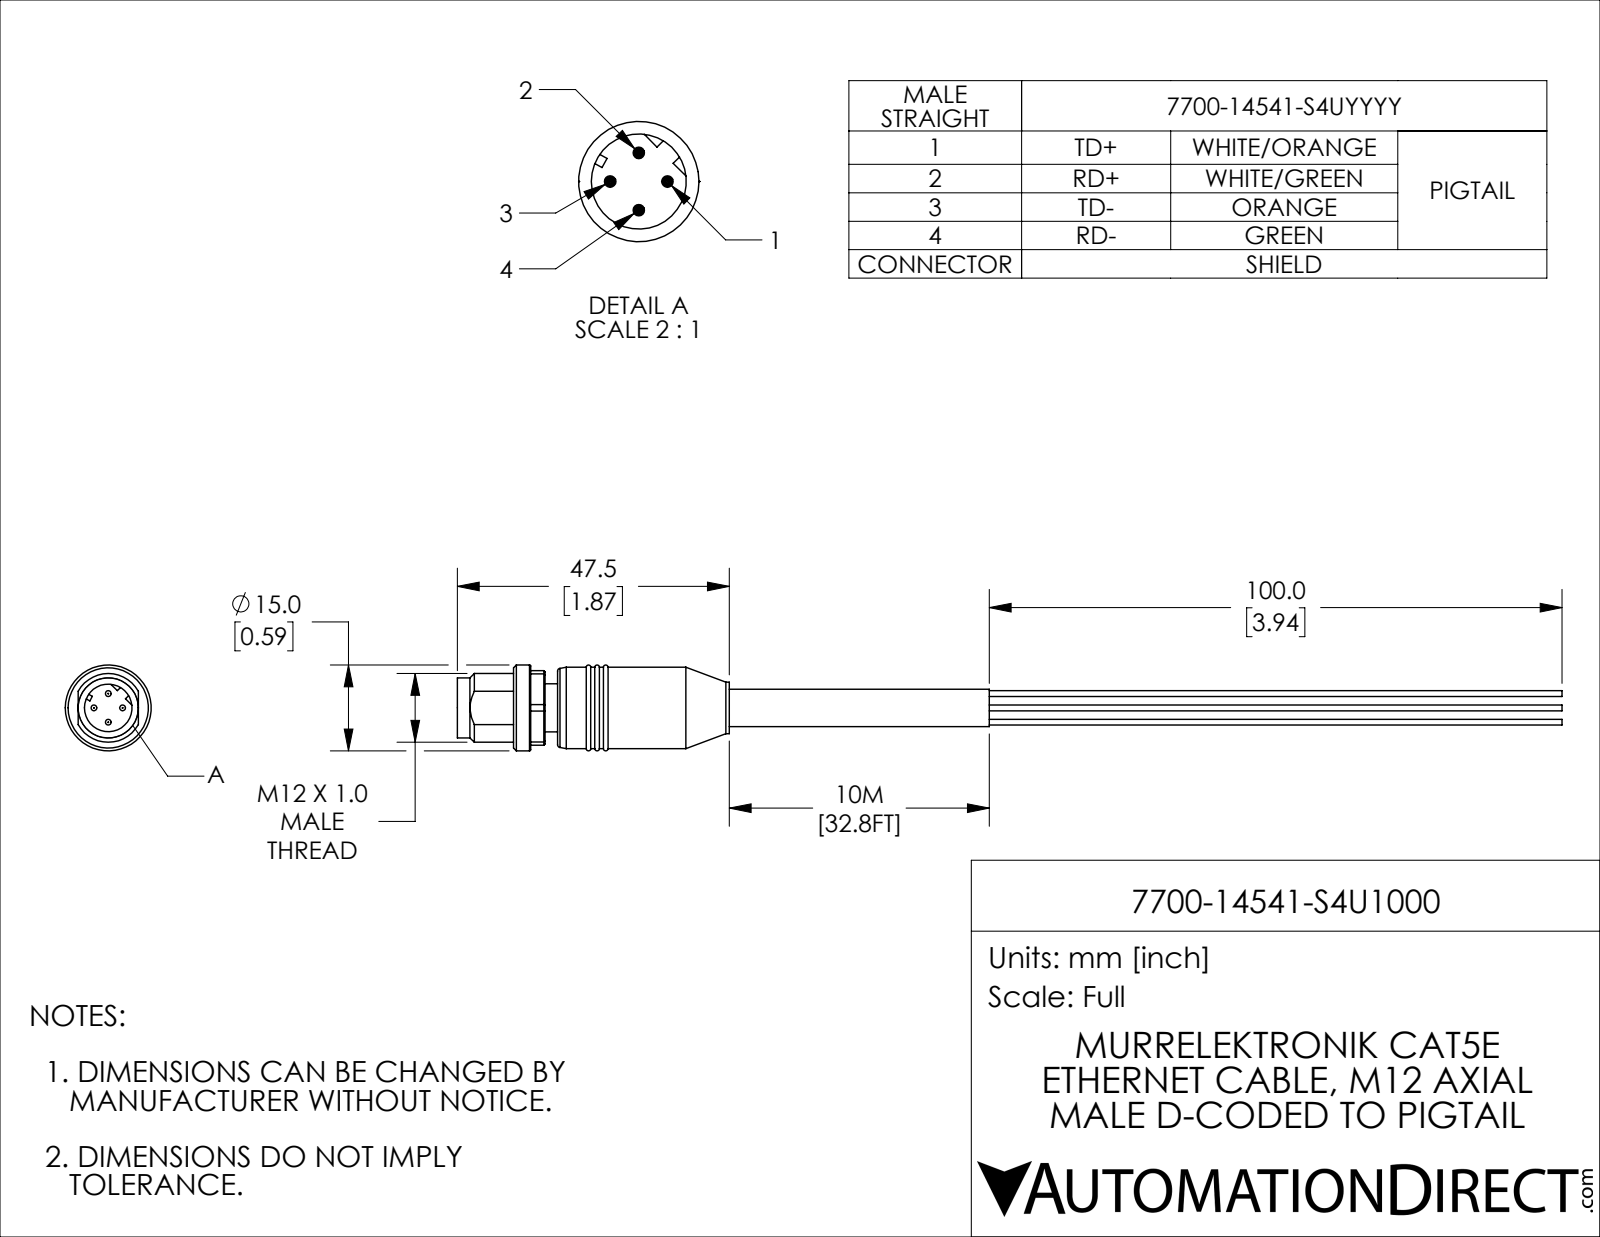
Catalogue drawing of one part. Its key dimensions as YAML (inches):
part_name: "7700-14541-S4U1000"
step_written_by: "SolidWorks 2021 (CONFIG_CONTROL_DESIGN)"
units: inches
bodies: {solids: 1, faces: 125, planar: 40, cylindrical: 45, other: 40}
overall_size: [7.594, 0.591, 0.591]
volume: 0.473
surface_area: 7.675
round_holes:
  - {diameter: 0.327, count: 1}
round_bosses_or_shafts:
  - {diameter: 0.039, count: 4}
  - {diameter: 0.591, count: 1}
  - {diameter: 0.559, count: 1}
  - {diameter: 0.413, count: 1}
  - {diameter: 0.354, count: 1}
  - {diameter: 0.331, count: 1}
  - {diameter: 0.256, count: 1}
partial_cylinders:
  - {radius: 0.236, count: 1}
  - {radius: 0.283, count: 1}
face_to_face_distances: [0.087, 0.035, 0.252, 0.339, 0.217, 0.303, 0.512, 0.413, 0.35, 0.386]
